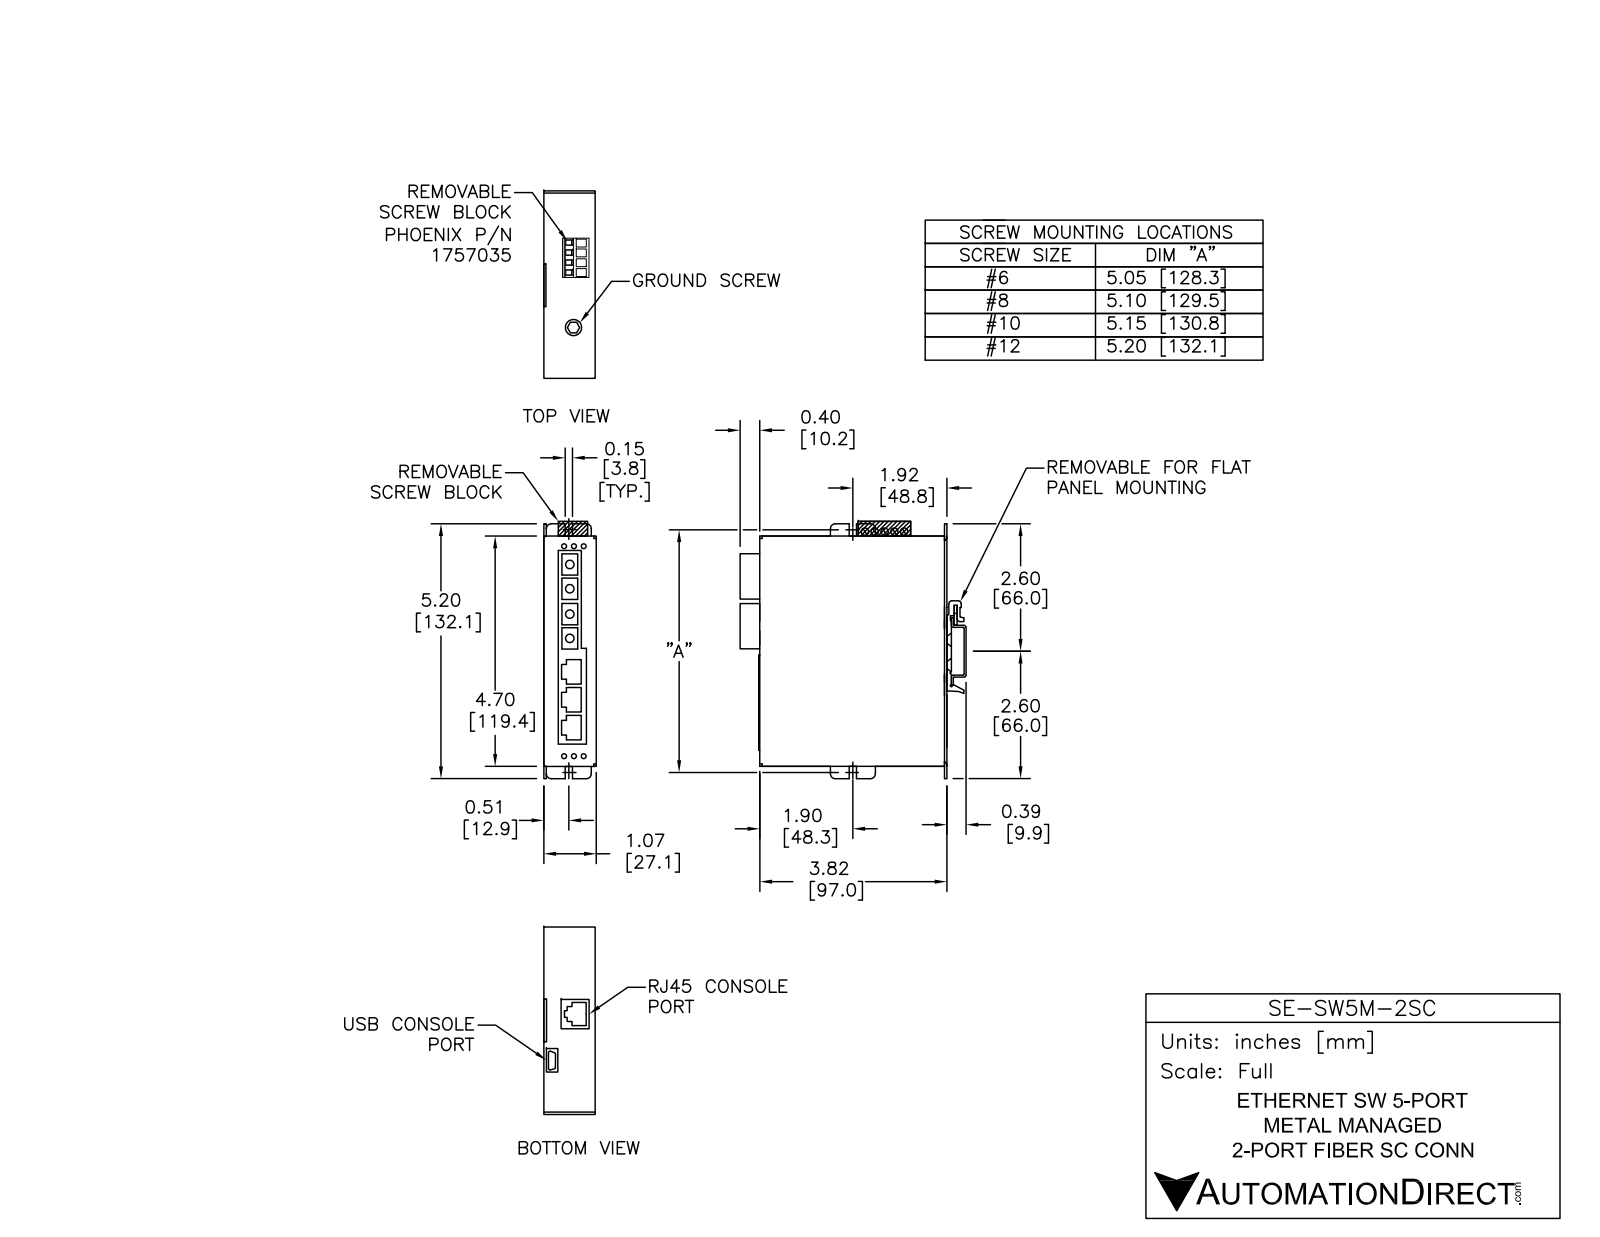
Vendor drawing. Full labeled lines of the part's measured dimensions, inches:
Part name (STEP PRODUCT): SE-SW5M-2SC
STEP written by: SolidWorks 2011 (AUTOMOTIVE_DESIGN)
Units: inches
Bodies: 1 solid, 366 faces (320 planar, 46 cylindrical, 0 other)
Overall size (bounding box): 5.38 × 4.636 × 1.07
Volume: 19.52 in³ · Surface area: 106.5 in²
Round holes (diameter × count): ⌀0.11 ×4, ⌀0.15 ×4, ⌀0.215 ×1
Round bosses / shafts (diameter × count): ⌀0.33 ×1
Partial cylindrical surfaces — rounded edges, fillets, slot ends (radius × count): R0.1 ×8, R0.03 ×7, R0.042 ×4, R0.045 ×4, R0.07 ×4, R0.06 ×3, R0.075 ×1, R0.076 ×1
Main face-to-face distances: 0.054, 1.07, 0.055, 1.015, 1.016, 0.055, 4.7, 3.82, 3.766, 3.765
Hole centre spacings: 0.185, 0.37, 0.164, 0.176, 0.341, 0.555, 4.41, 4.414
